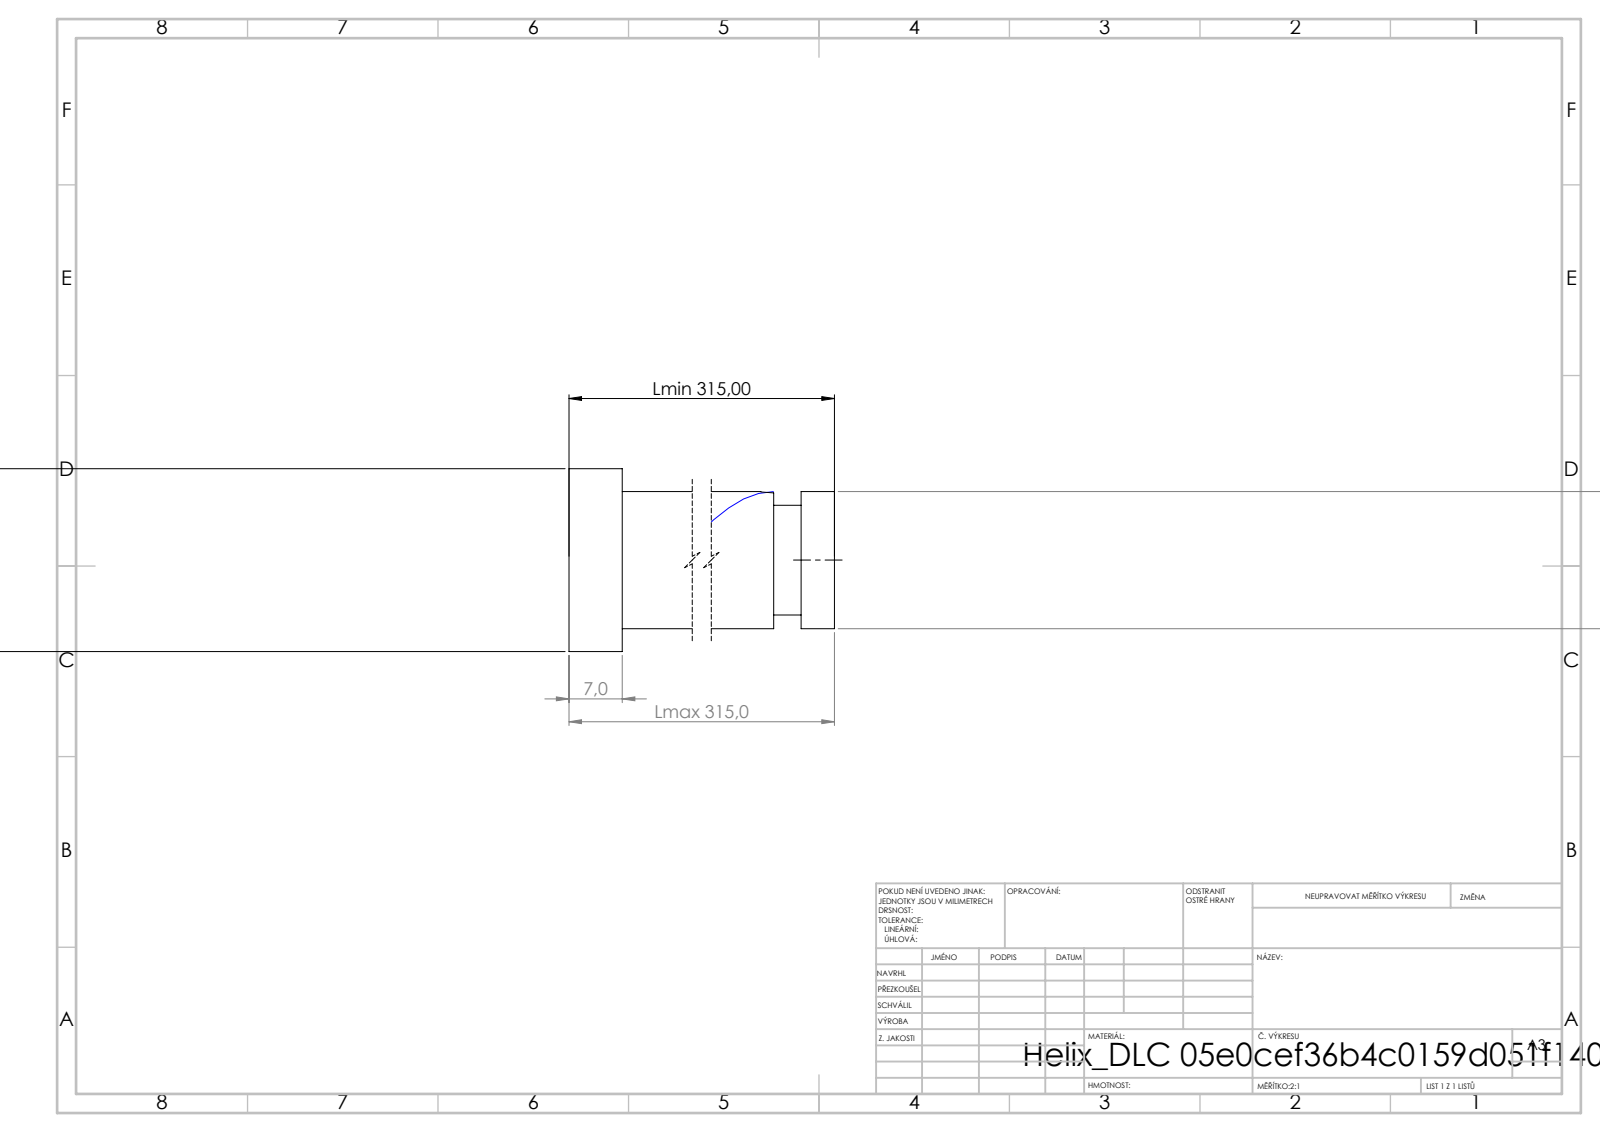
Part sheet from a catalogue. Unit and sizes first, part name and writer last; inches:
Units: inches
Overall size (bounding box): 12.402 × 0.945 × 0.945
Round bosses / shafts (diameter × count): ⌀0.945 ×1, ⌀0.709 ×1, ⌀0.567 ×1
Main face-to-face distances: 12.402, 0.276, 12.126, 12.229, 11.954, 0.172, 12.087, 11.812, 0.142, 0.314
Volume: 4.909 in³ · Surface area: 30.15 in²
Bodies: 1 solid, 21 faces (6 planar, 14 cylindrical, 1 other)
STEP written by: SolidWorks 2019 (CONFIG_CONTROL_DESIGN)
